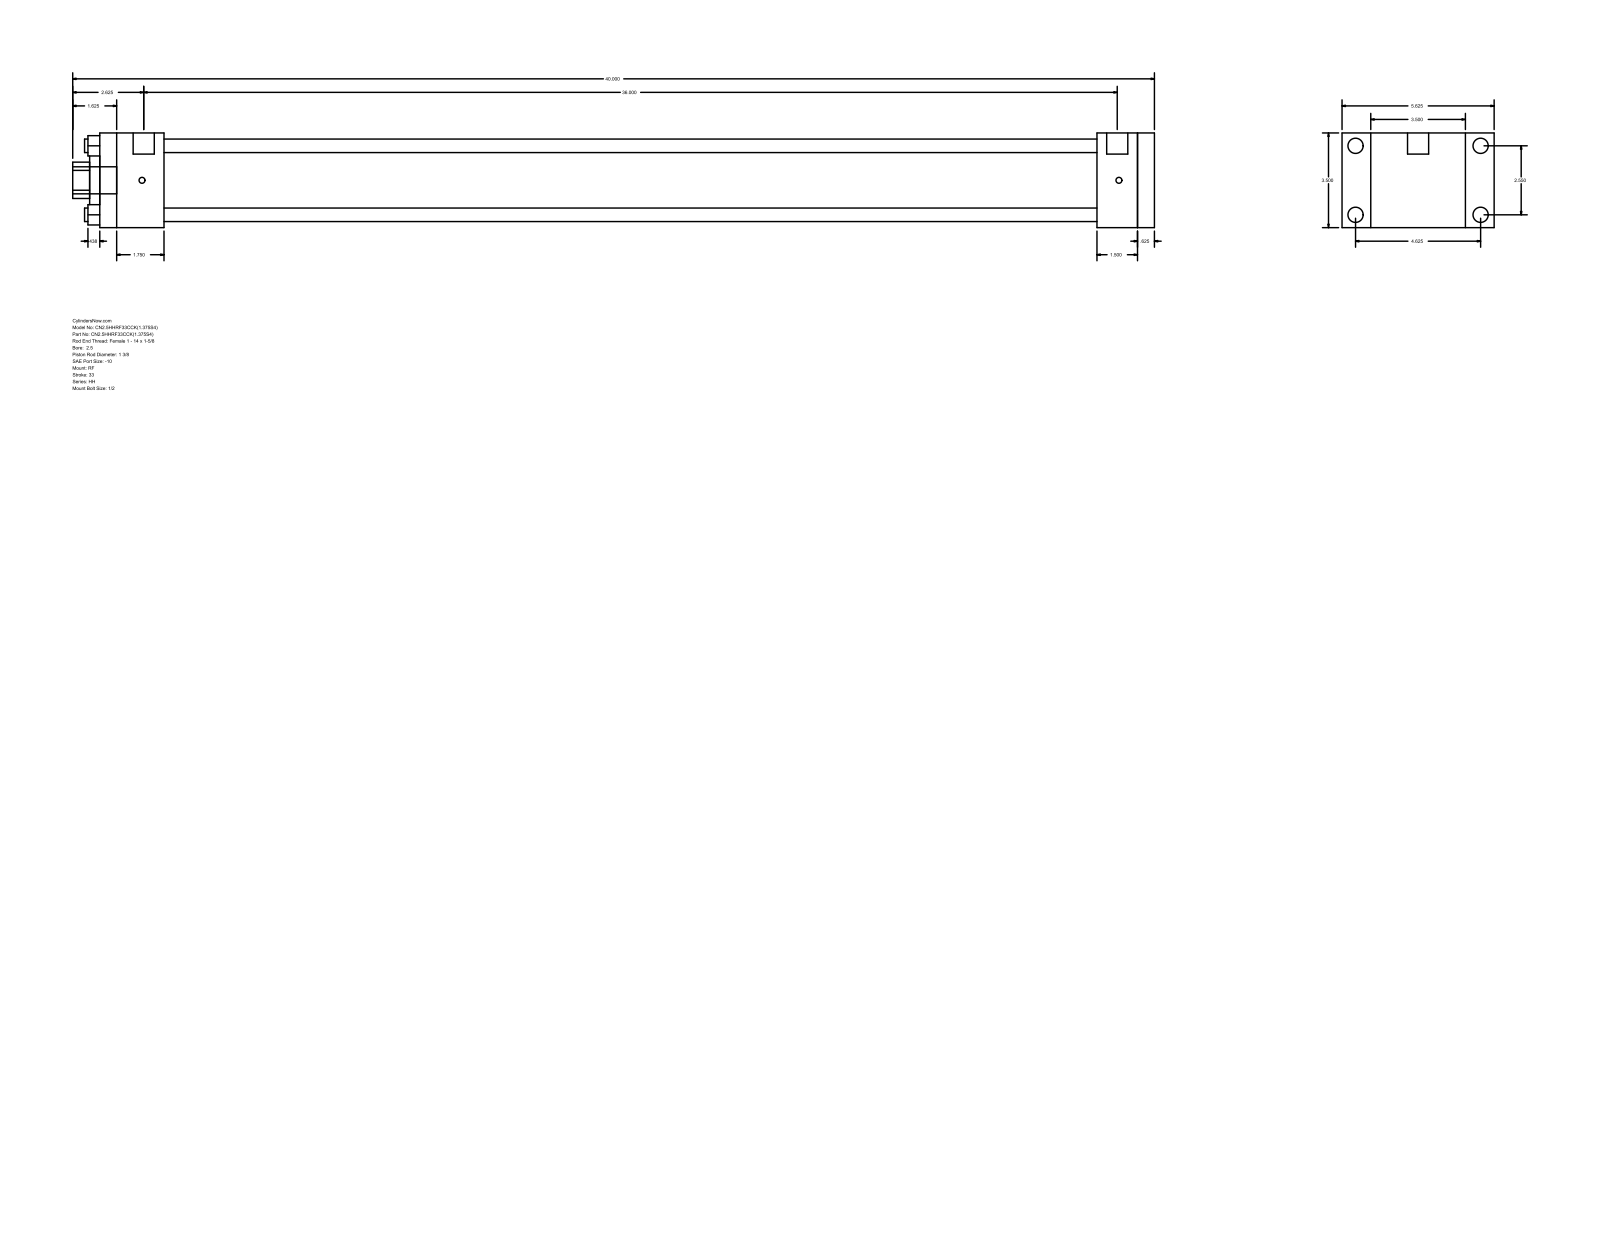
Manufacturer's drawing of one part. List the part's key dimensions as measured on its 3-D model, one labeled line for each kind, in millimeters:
Part name (STEP PRODUCT): HH_RF__0250_1.375
STEP written by: GSSL Pune (CONFIG_CONTROL_DESIGN)
Units: millimetres
Bodies: 0 solids, 92 faces (64 planar, 28 cylindrical, 0 other)
Overall size (bounding box): 1016 × 142.88 × 88.9
Round holes (diameter × count): ⌀12.7 ×4, ⌀34.92 ×1, ⌀50.8 ×1, ⌀73.03 ×1
Round bosses / shafts (diameter × count): ⌀14.3 ×4, ⌀5.56 ×4, ⌀19.84 ×2, ⌀25.4 ×1
Partial cylindrical surfaces — rounded edges, fillets, slot ends (radius × count): R17.06 ×1
Main face-to-face distances: 88.9, 990.6, 15.88, 974.72, 60.32, 914.4, 930.28, 936.62, 876.3, 38.1
Hole centre spacings: 45.79, 64.76, 91.58
